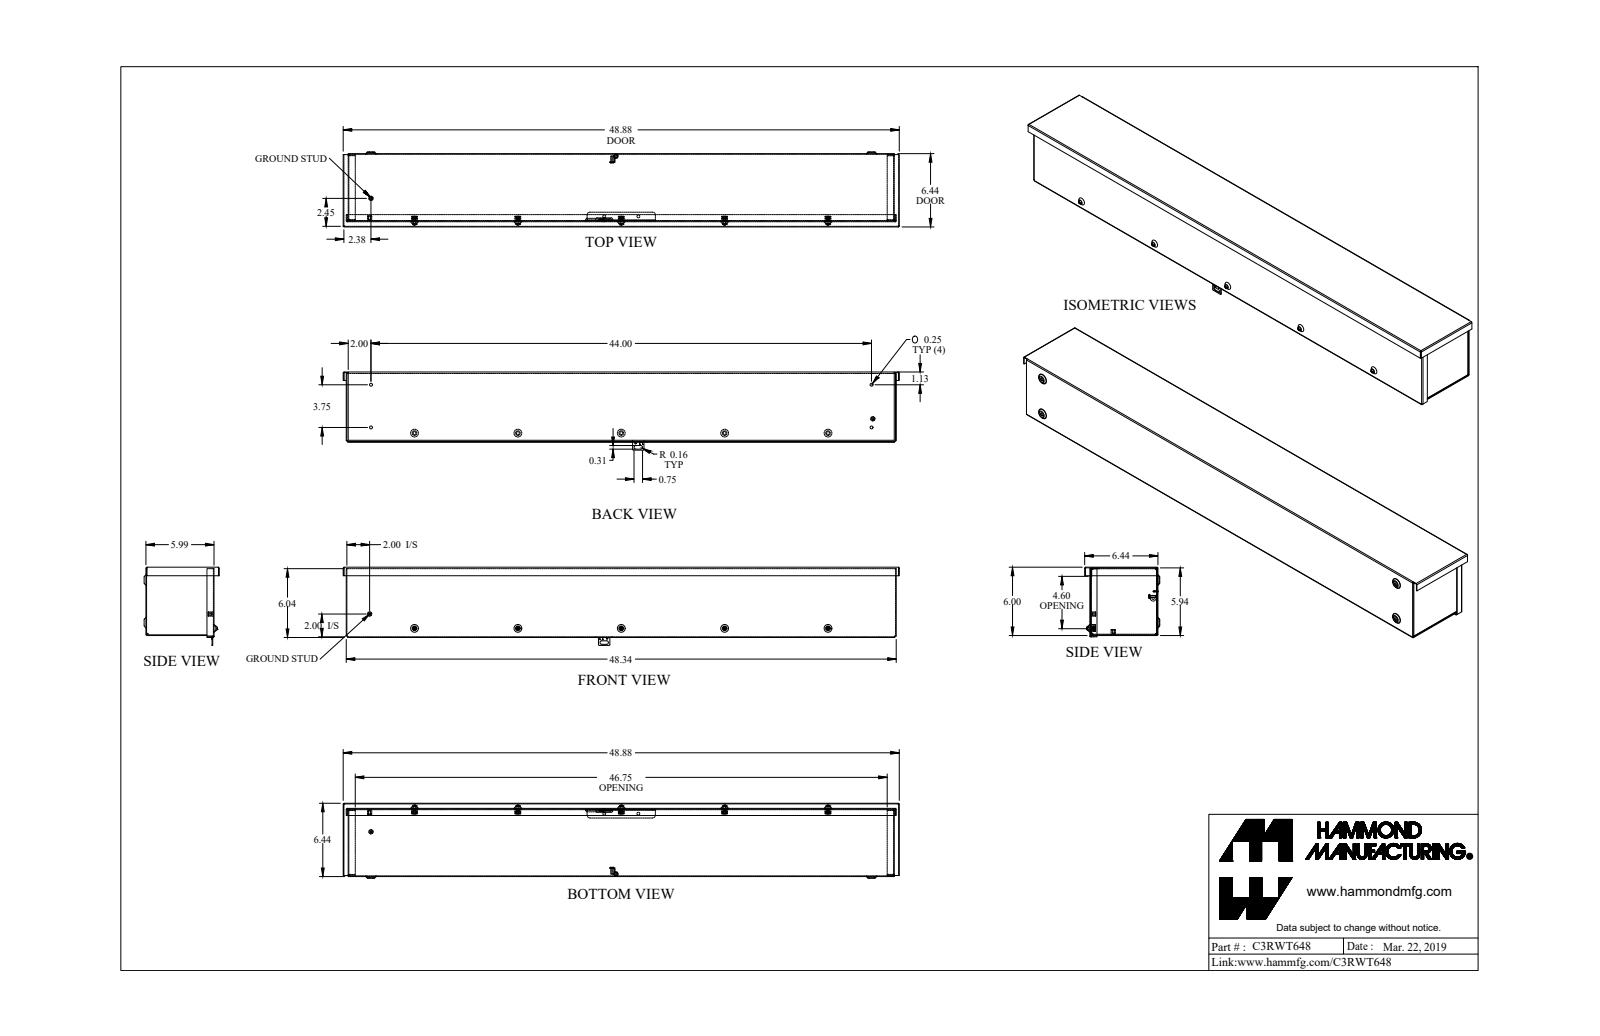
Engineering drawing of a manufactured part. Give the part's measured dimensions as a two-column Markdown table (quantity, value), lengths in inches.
| quantity | value |
| --- | --- |
| part name | C3RWT648_Default |
| STEP written by | SolidWorks 2019 (CONFIG_CONTROL_DESIGN) |
| units | inches |
| bodies | 28 solids, 1008 faces (557 planar, 315 cylindrical, 136 other) |
| overall size | 48.875 × 6.871 × 6.594 |
| volume | 79.66 in³ |
| surface area | 2 815 in² |
| round holes (diameter × count) | 0.156 × 7, 0.25 × 6, 0.214 × 5, 0.23 × 5, 0.203 × 2, 0.125 × 1, 0.137 × 1, 0.2 × 1, 0.215 × 1 |
| round bosses / shafts (diameter × count) | 0.19 × 6, 0.148 × 5, 0.375 × 2, 0.5 × 1, 0.367 × 1, 0.21 × 1, 0.152 × 1, 0.125 × 1 |
| partial cylindrical surfaces (radius × count) | 0.08 × 20, 0.108 × 20, 0.029 × 18, 0.086 × 18, 0.125 × 15, 0.022 × 10, 0.25 × 6, 0.171 × 5 |
| main face-to-face distances | 0.057, 5.943, 5.928, 5.871, 5.886, 5.985, 6, 47.943, 6.381, 0.51 |
| hole center spacings | 9.086, 9.086, 18.172, 27.258, 3.488, 6.95, 12.924, 15.582 |
